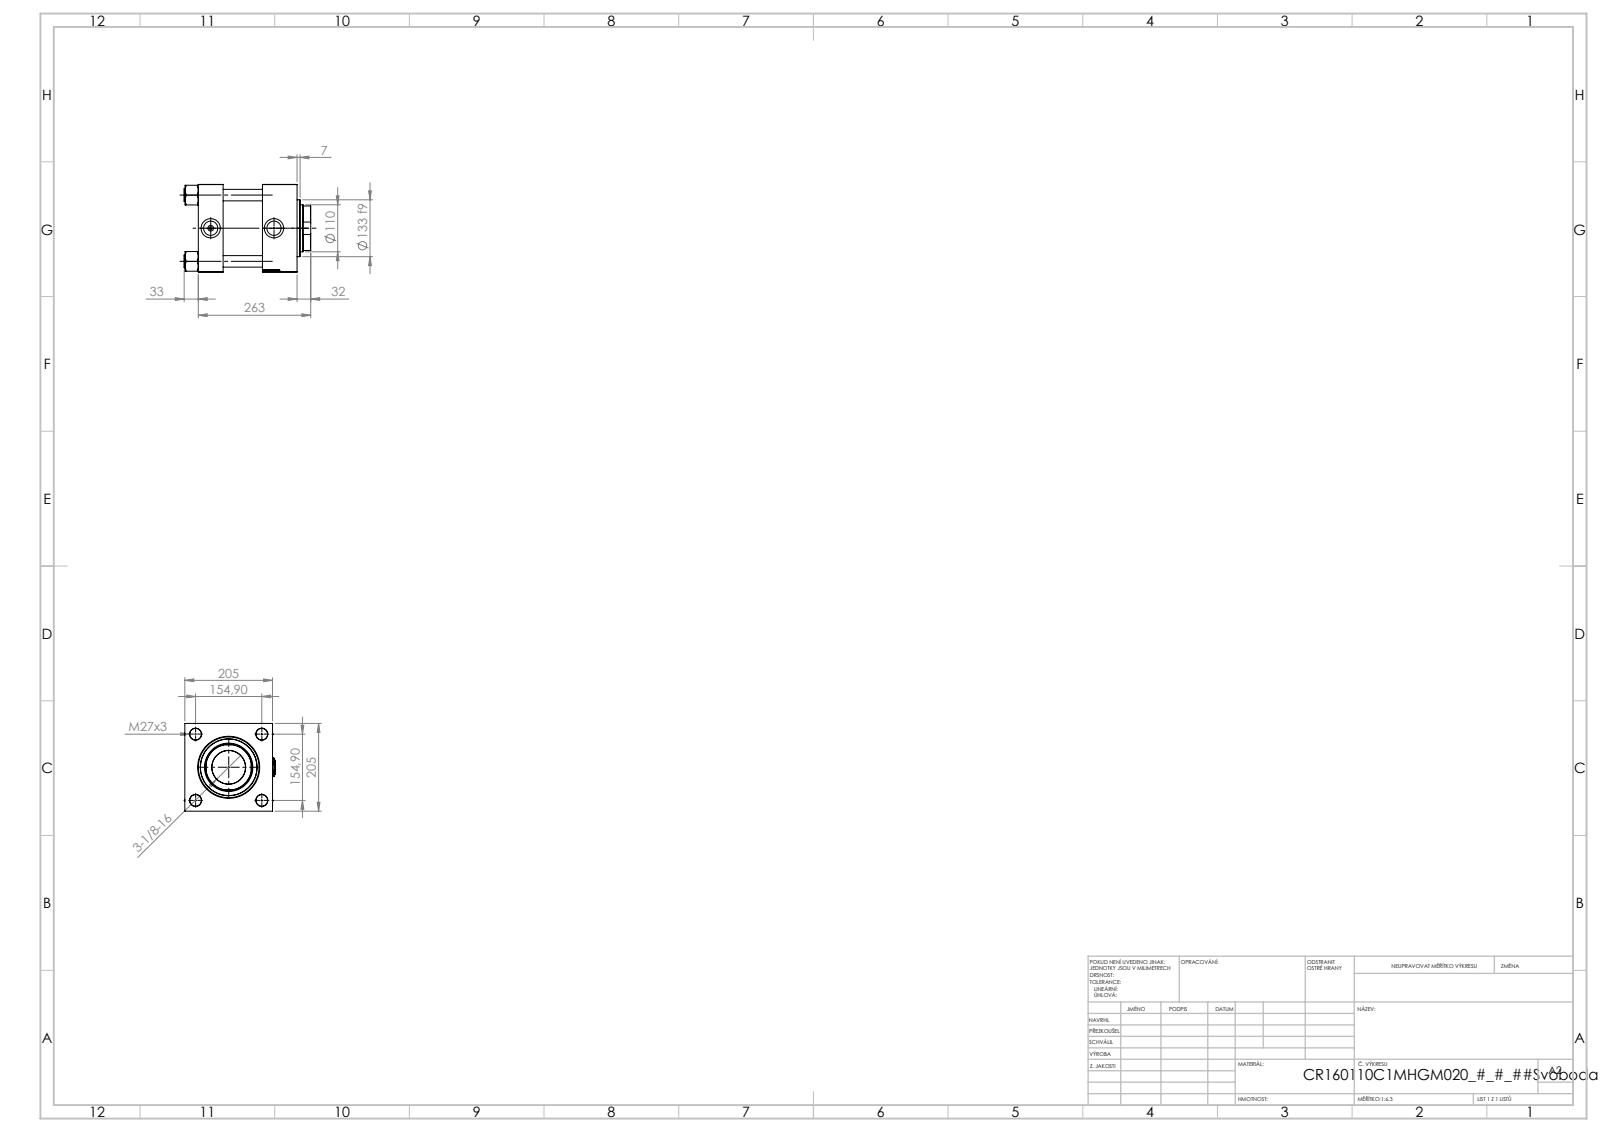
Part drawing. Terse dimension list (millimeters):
name: Zatka_pro_OIL_PORT; V215CR_VCP_C; V215CR_C_Body; NUT_M5_C (+2 more)
written by: SolidWorks 2019 (CONFIG_CONTROL_DESIGN)
unit: mm
bodies: 12 solids, 1243 faces (597 planar, 90 cylindrical, 556 other)
size: 296 × 213.57 × 205
volume: 7 621 000 mm³; area: 726 425 mm²
holes: 4× ⌀27, 2× ⌀7, 2× ⌀33.24, 2× ⌀45, 1× ⌀78.5, 1× ⌀110, 1× ⌀113, 1× ⌀120, 1× ⌀142, 1× ⌀160
bosses: 4× ⌀30, 1× ⌀166, 1× ⌀133
rounds: 1× R54
face distances: 205, 58, 150, 92, 231, 173, 81, 202.3, 144.3, 52.3
hole spacings: 109.53, 154.9, 219.06, 148
